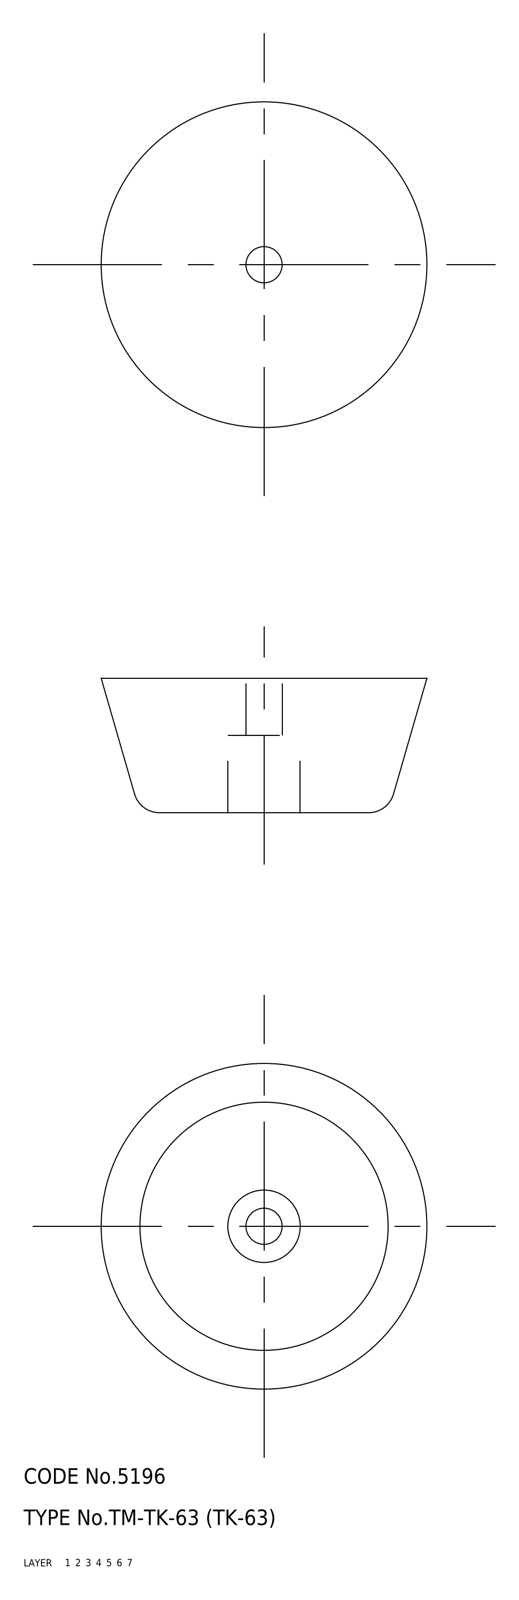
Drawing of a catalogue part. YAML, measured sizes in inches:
part_name: "washer; rubber foot; TK_63_10012_36"
step_written_by: "CADfix (AUTOMOTIVE_DESIGN)"
units: inches
bodies: {solids: 2, faces: 23, planar: 0, cylindrical: 0, other: 23}
overall_size: [2.48, 2.48, 1.024]
volume: 3.68
surface_area: 17.34
